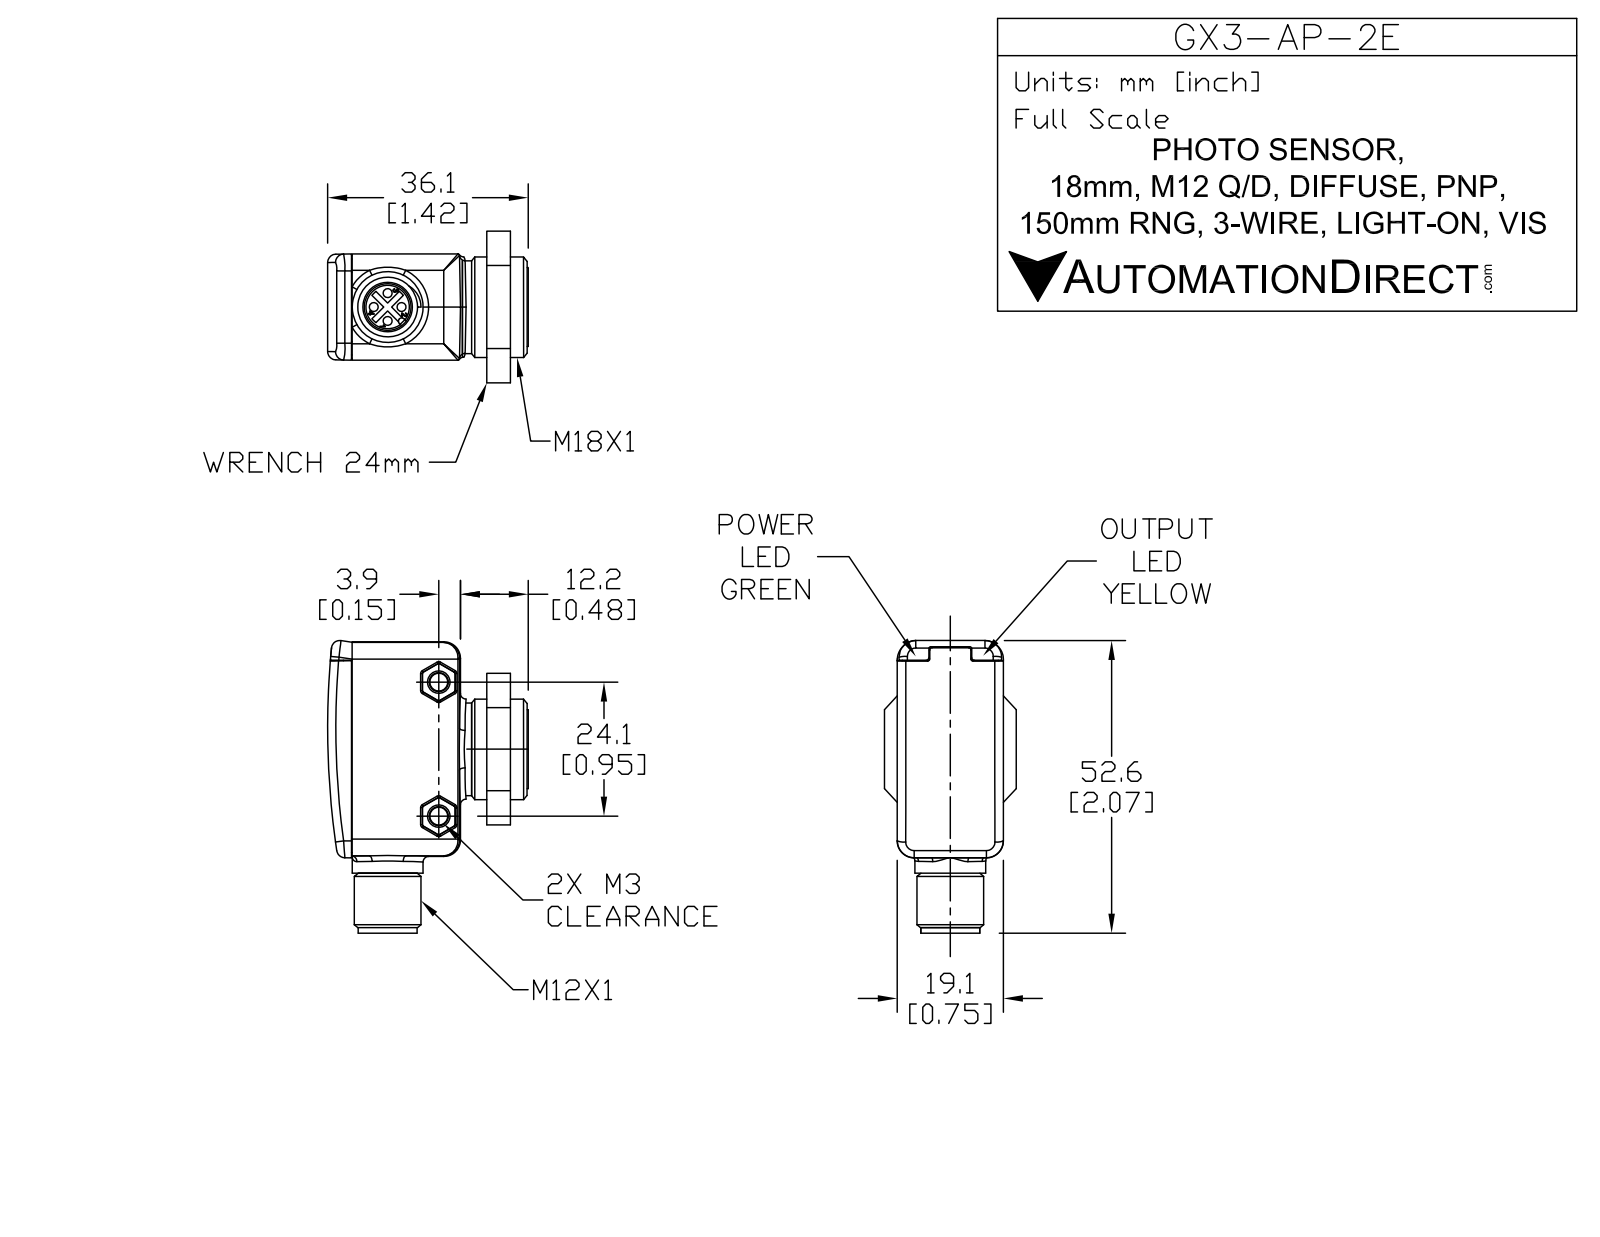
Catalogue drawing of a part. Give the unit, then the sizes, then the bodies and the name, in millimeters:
Units: millimetres
Overall size (bounding box): 52.66 × 36.1 × 23.85
Round holes (diameter × count): ⌀3.2 ×2, ⌀8.36 ×1
Round bosses / shafts (diameter × count): ⌀18 ×1, ⌀17.5 ×1, ⌀14.2 ×1, ⌀12.68 ×1, ⌀11.55 ×1, ⌀10.6 ×1
Partial cylindrical surfaces — rounded edges, fillets, slot ends (radius × count): R1.5 ×8, R1 ×4, R139.57 ×1
Main face-to-face distances: 19.1, 7.2, 2.12, 9.32, 19.2, 5, 2.88, 12.2, 38.8, 5.95
Hole centre spacings: 24.1
Volume: 21 253 mm³ · Surface area: 6 452 mm²
Bodies: 1 solid, 107 faces (60 planar, 33 cylindrical, 14 other)
Part name (STEP PRODUCT): GX3-AP-2E
STEP written by: SolidWorks 2013 (AUTOMOTIVE_DESIGN)
